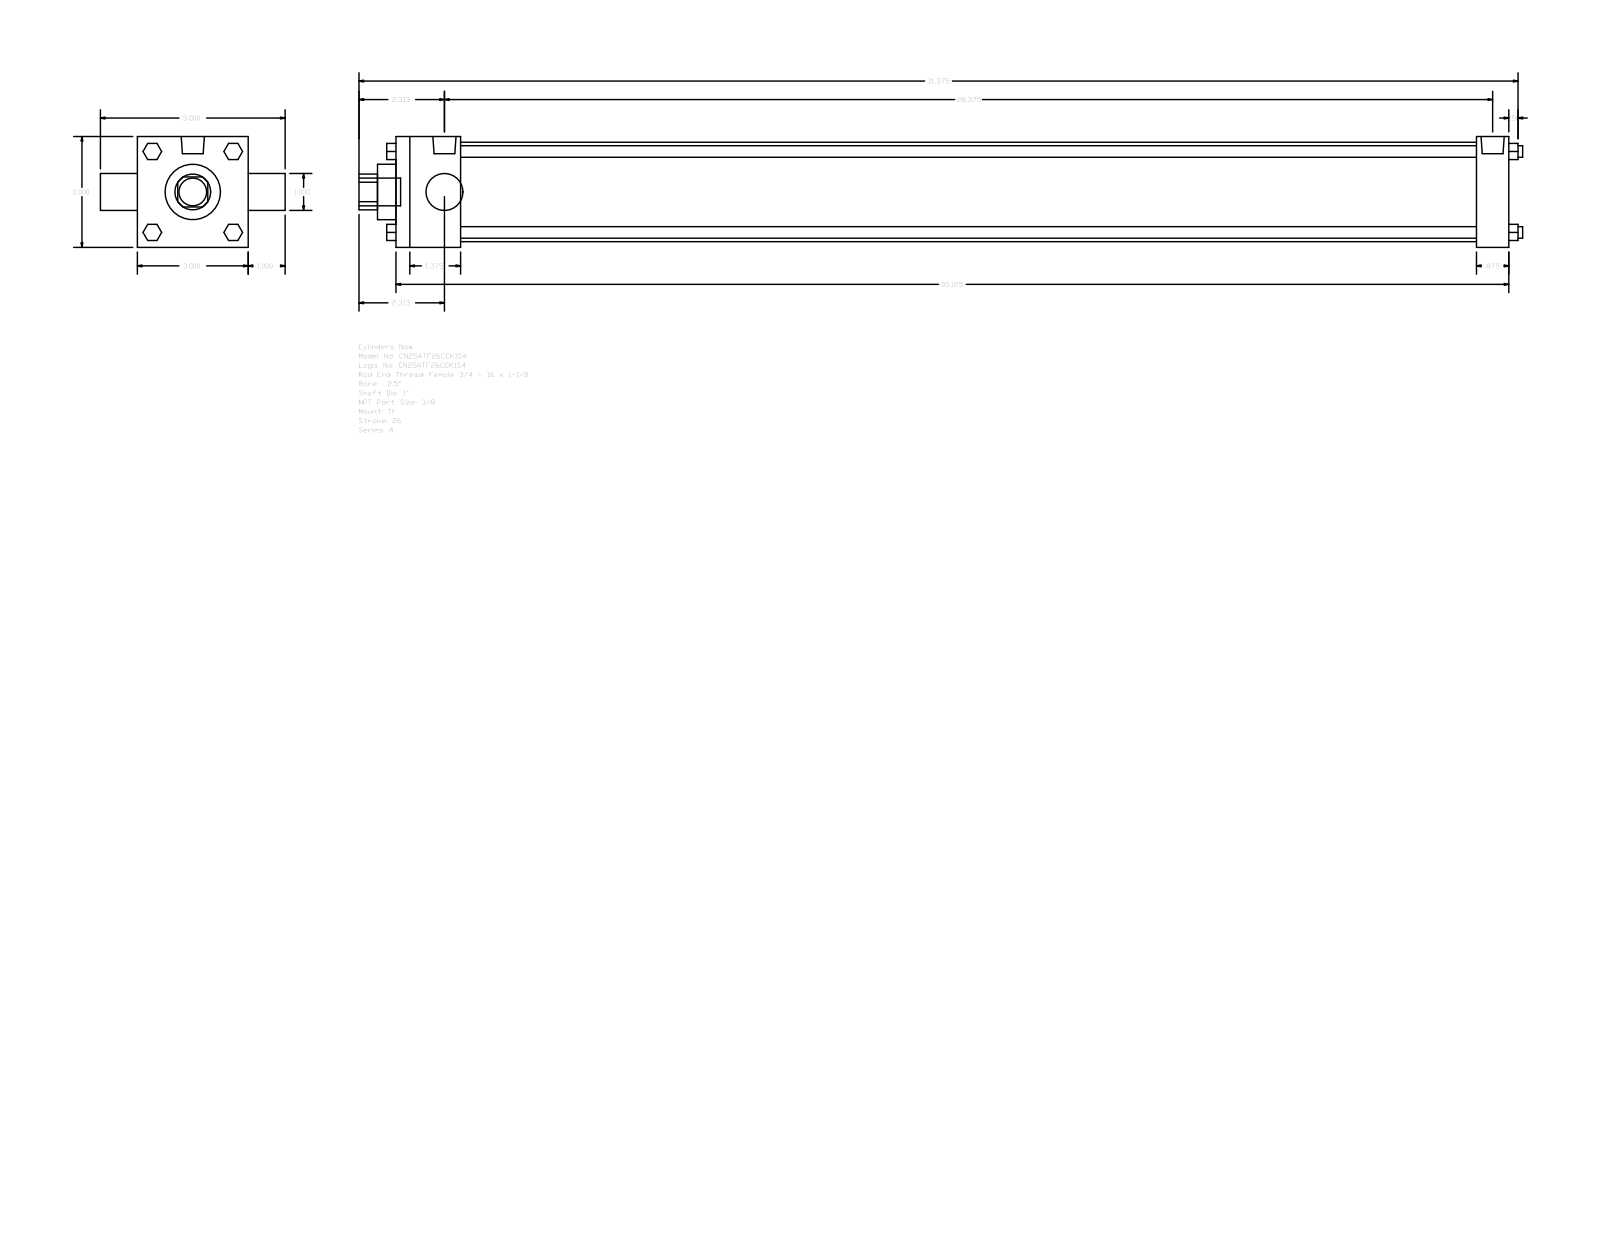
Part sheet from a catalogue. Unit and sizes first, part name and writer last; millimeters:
Units: millimetres
Overall size (bounding box): 800.1 × 127 × 76.2
Round holes (diameter × count): ⌀25.4 ×2, ⌀38.1 ×1, ⌀68.33 ×1
Round bosses / shafts (diameter × count): ⌀7.94 ×4, ⌀5.56 ×3, ⌀15.93 ×2, ⌀19.05 ×1
Partial cylindrical surfaces — rounded edges, fillets, slot ends (radius × count): R12.29 ×1
Main face-to-face distances: 76.2, 765.18, 44.45, 742.95, 698.5, 720.73, 22.23, 25.4, 101.6, 12.7
Bodies: 0 solids, 120 faces (92 planar, 28 cylindrical, 0 other)
Part name (STEP PRODUCT): A_TF__0250_1
STEP written by: GSSL Pune (CONFIG_CONTROL_DESIGN)
